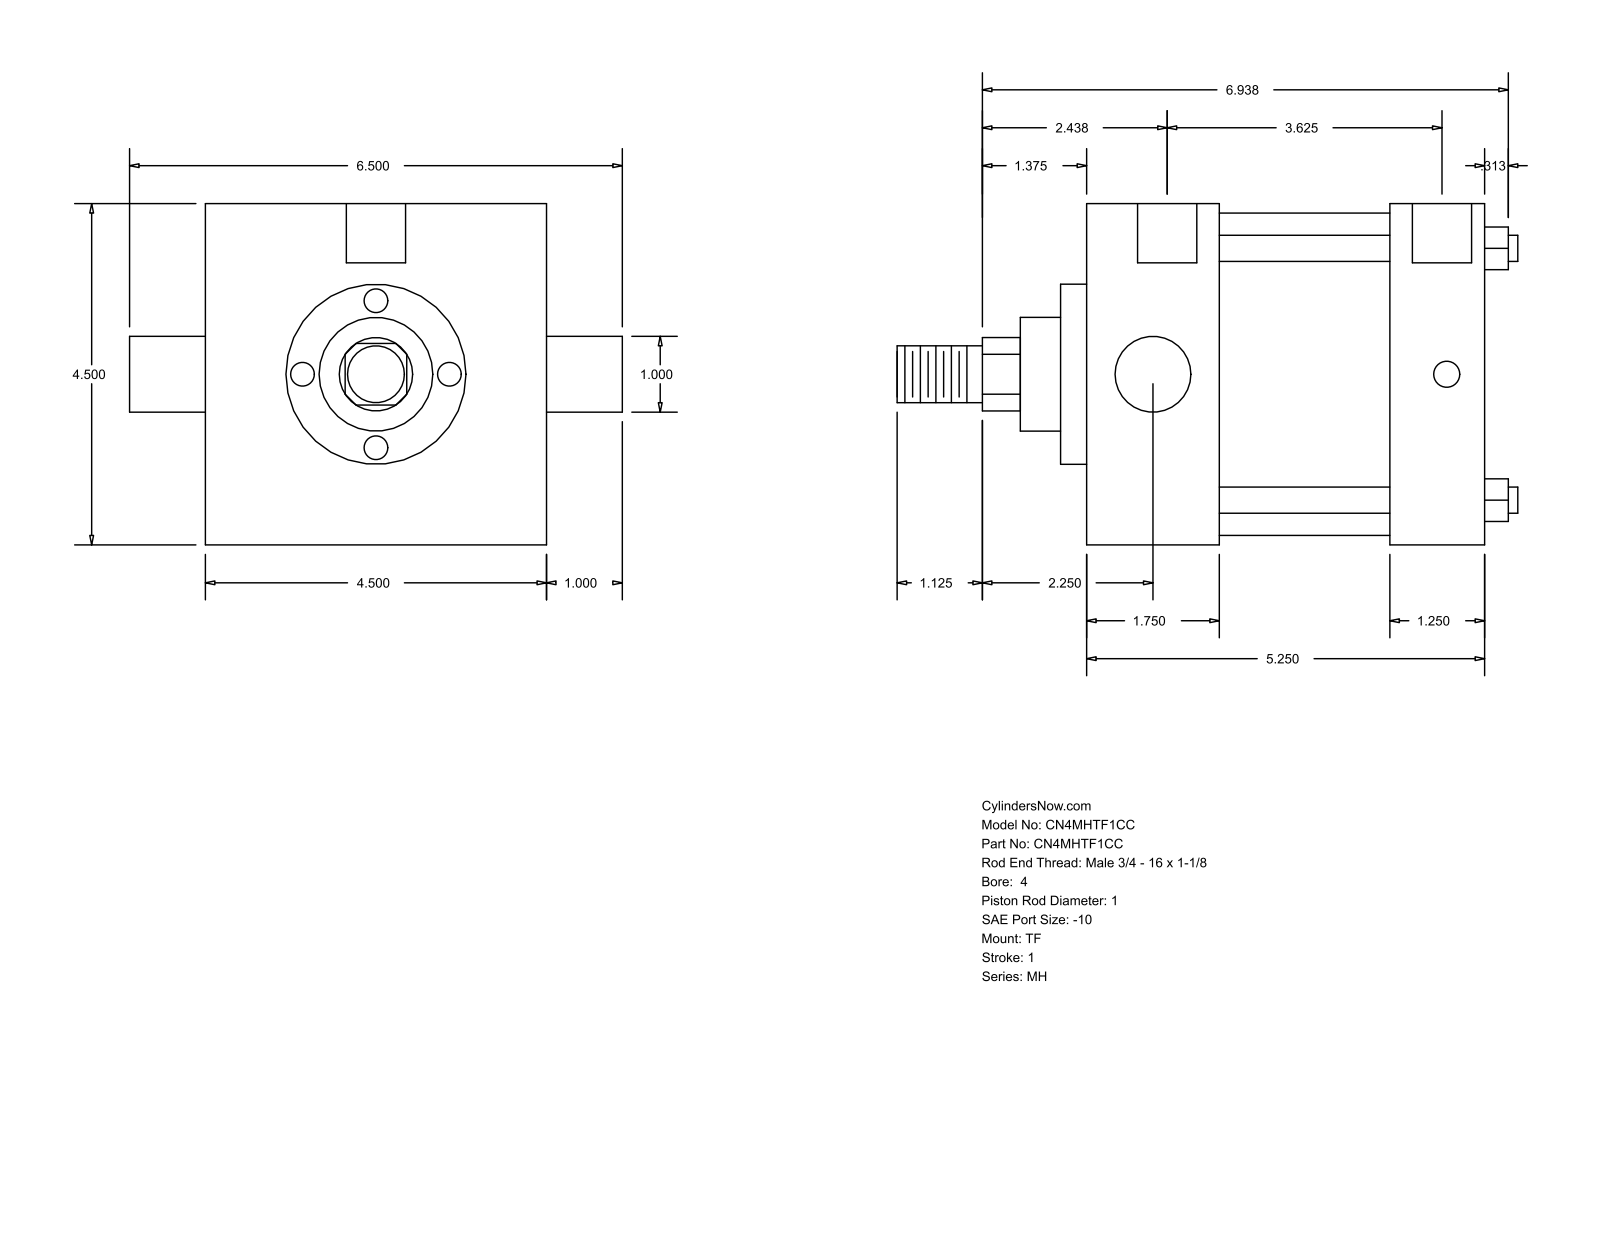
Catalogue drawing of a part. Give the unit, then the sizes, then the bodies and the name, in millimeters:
Units: millimetres
Overall size (bounding box): 207.96 × 165.1 × 114.3
Round holes (diameter × count): ⌀8.73 ×3, ⌀19.84 ×2
Round bosses / shafts (diameter × count): ⌀8.76 ×4, ⌀25.4 ×2, ⌀107.95 ×1, ⌀60.33 ×1, ⌀38.1 ×1, ⌀19.05 ×1
Partial cylindrical surfaces — rounded edges, fillets, slot ends (radius × count): R12.29 ×1
Main face-to-face distances: 114.3, 133.36, 44.46, 88.9, 101.61, 57.15, 31.75, 8.73, 53.19, 110.34
Hole centre spacings: 1.58, 93.66, 92.08, 95.24
Bodies: 0 solids, 86 faces (61 planar, 25 cylindrical, 0 other)
Part name (STEP PRODUCT): MH_TF__0400_1
STEP written by: GSSL Pune (CONFIG_CONTROL_DESIGN)
